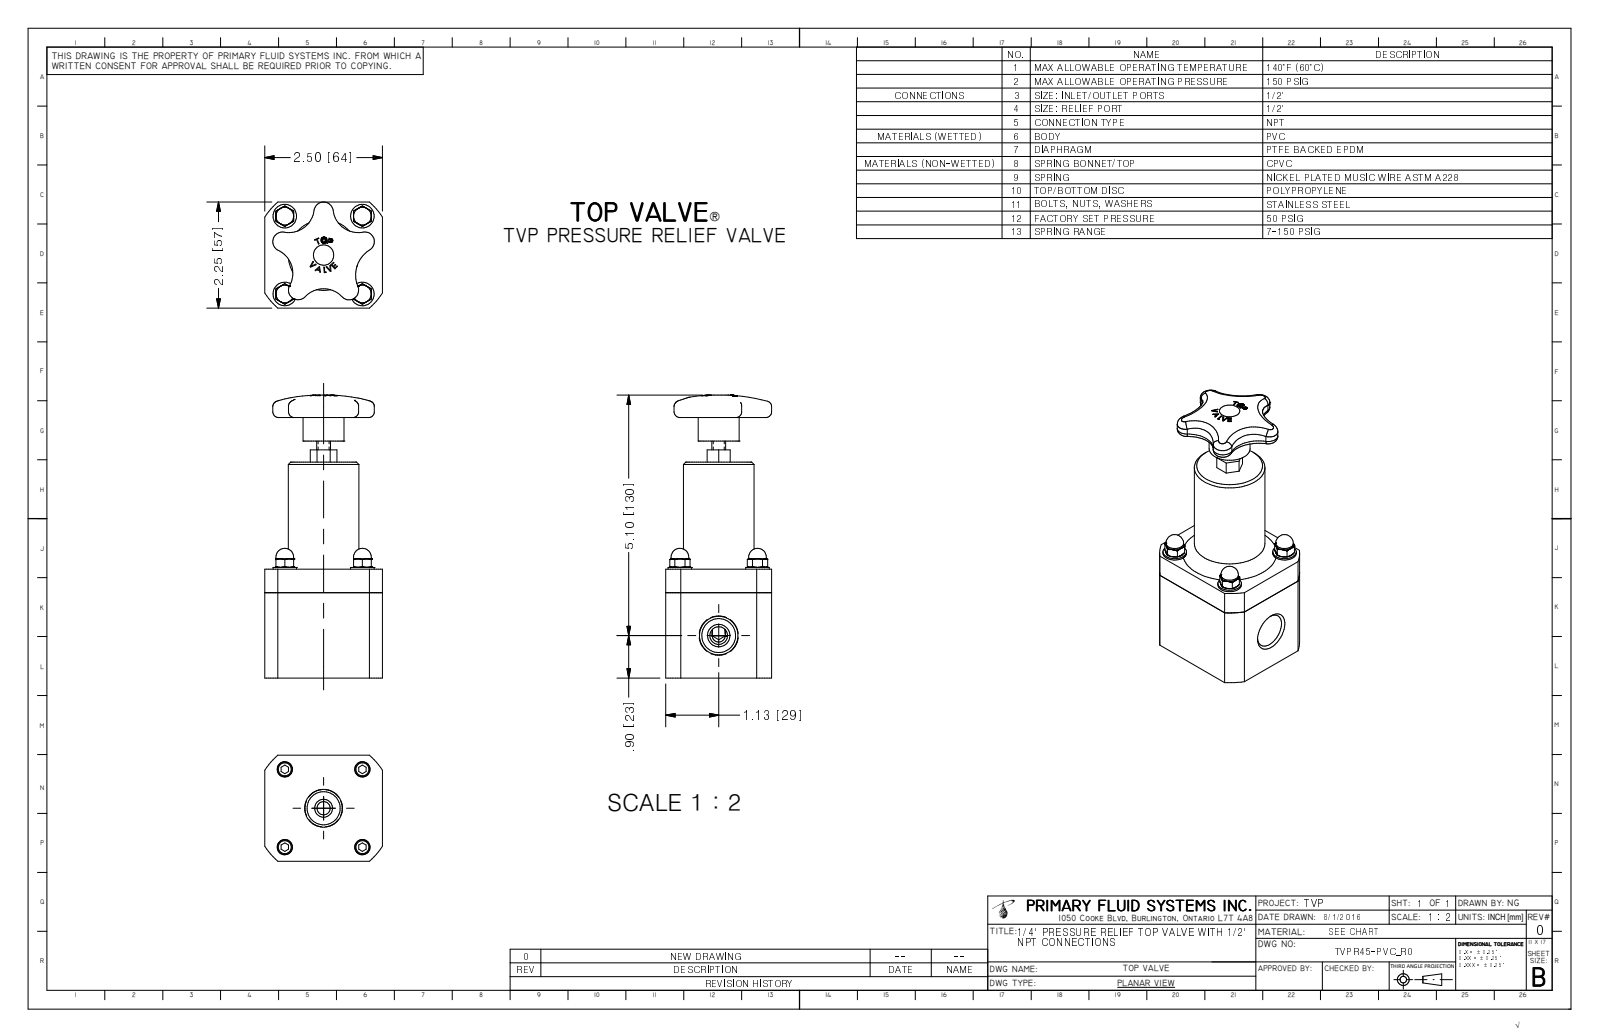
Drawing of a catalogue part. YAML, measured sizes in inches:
part_name: "TVPR45-PVC_R0"
step_written_by: "Autodesk Inventor 2009 (AUTOMOTIVE_DESIGN)"
units: inches
bodies: {solids: 1, faces: 356, planar: 147, cylindrical: 48, other: 161}
overall_size: [6, 2.5, 2.25]
volume: 17.34
surface_area: 60.05
round_holes:
  - {diameter: 0.147, count: 4}
  - {diameter: 0.703, count: 1}
  - {diameter: 0.719, count: 1}
  - {diameter: 1.525, count: 1}
round_bosses_or_shafts:
  - {diameter: 0.5, count: 4}
  - {diameter: 0.375, count: 4}
  - {diameter: 0.312, count: 4}
  - {diameter: 1.5, count: 1}
  - {diameter: 0.87, count: 1}
  - {diameter: 0.293, count: 1}
partial_cylinders:
  - {radius: 0.085, count: 5}
  - {radius: 0.205, count: 5}
  - {radius: 0.536, count: 4}
  - {radius: 0.656, count: 4}
  - {radius: 0.625, count: 1}
  - {radius: 0.745, count: 1}
  - {radius: 1.488, count: 1}
face_to_face_distances: [2.25, 2.5, 2.31, 4.58, 2.27, 0.6, 1.9, 5.026, 2.716, 0.446]
hole_center_spacings: [1.167, 1.167, 1.65, 1.65, 2.334]
